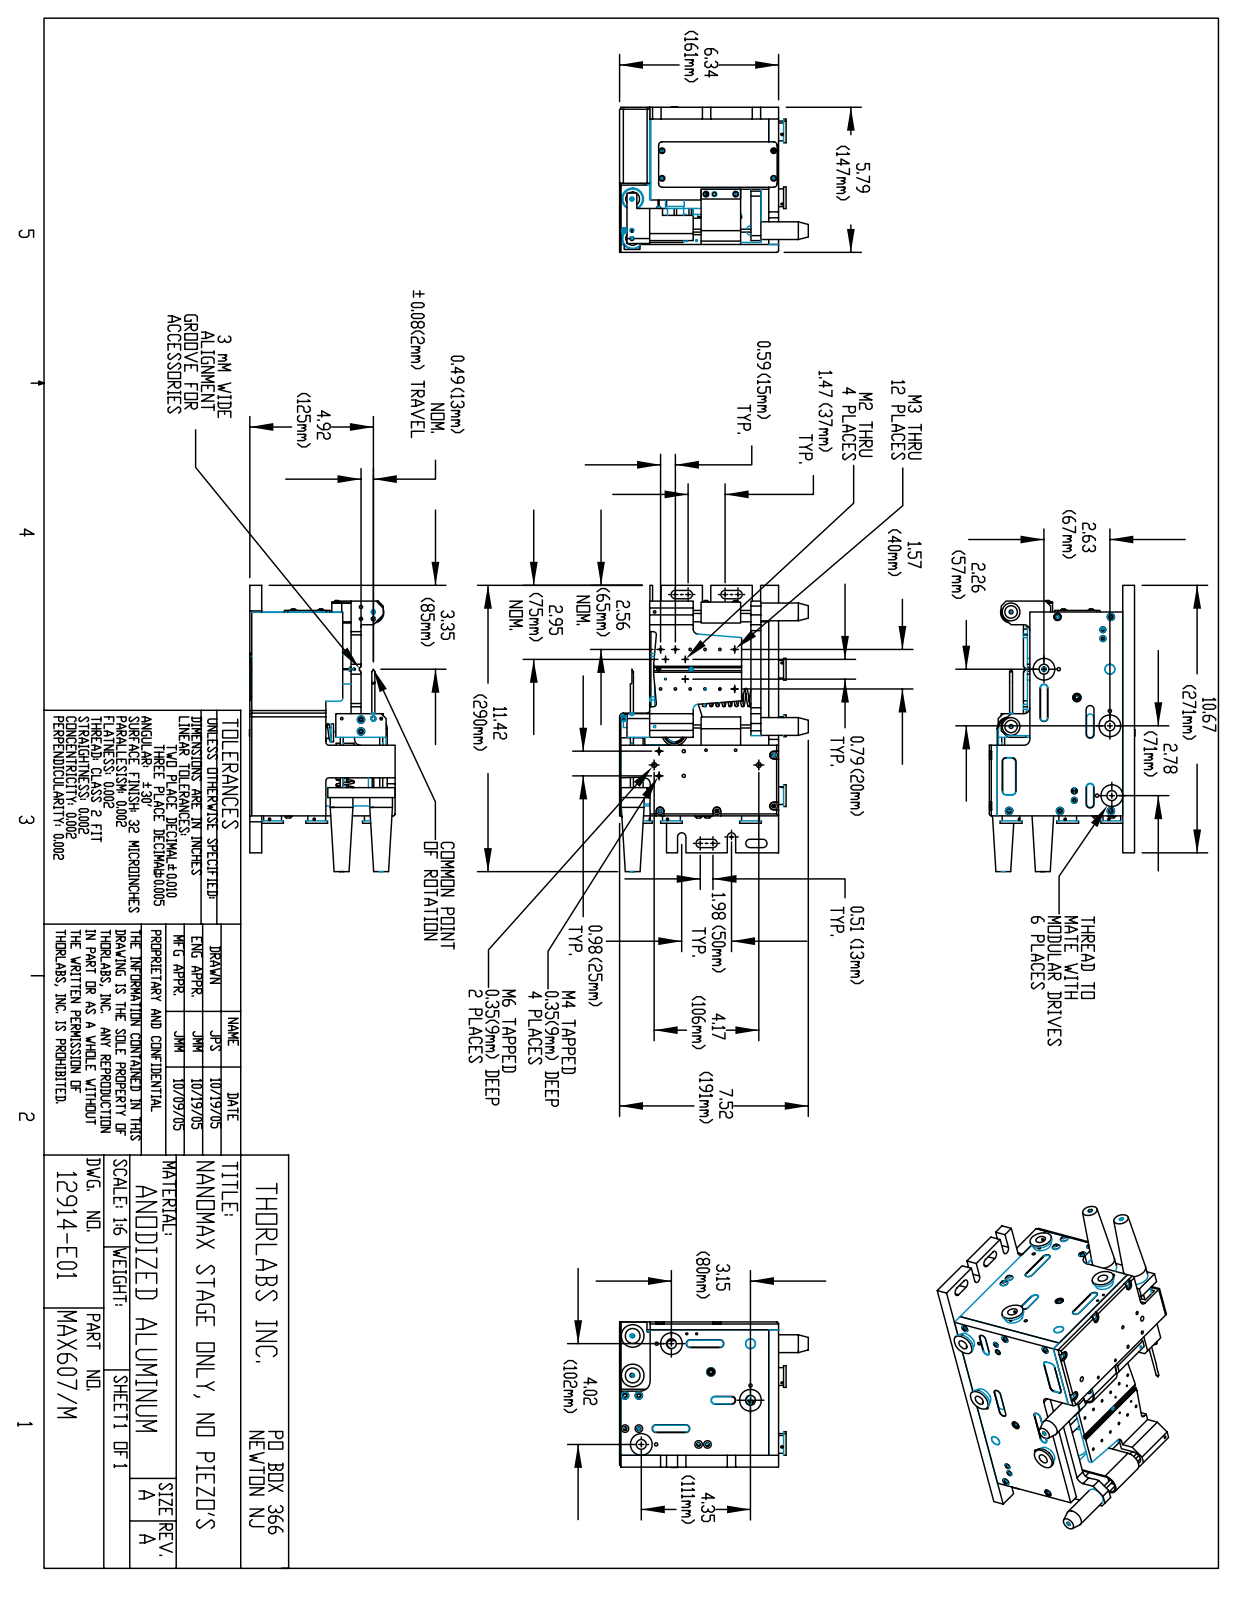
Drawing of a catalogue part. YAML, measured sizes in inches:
part_name: "12914-E0W"
step_written_by: "SolidWorks 2007 (AUTOMOTIVE_DESIGN)"
units: inches
bodies: {solids: 0, faces: 1185, planar: 615, cylindrical: 410, other: 160}
overall_size: [11.417, 7.52, 5.803]
round_holes:
  - {diameter: 0.098, count: 24}
  - {diameter: 0.295, count: 14}
  - {diameter: 0.13, count: 9}
  - {diameter: 0.394, count: 7}
  - {diameter: 0.236, count: 6}
  - {diameter: 0.291, count: 5}
  - {diameter: 0.063, count: 4}
  - {diameter: 0.126, count: 4}
  - {diameter: 0.157, count: 4}
  - {diameter: 0.551, count: 4}
  - {diameter: 0.081, count: 3}
  - {diameter: 0.335, count: 3}
round_bosses_or_shafts:
  - {diameter: 0.709, count: 11}
  - {diameter: 0.299, count: 8}
  - {diameter: 0.866, count: 6}
  - {diameter: 0.224, count: 6}
  - {diameter: 0.118, count: 6}
  - {diameter: 0.315, count: 5}
  - {diameter: 0.276, count: 4}
  - {diameter: 0.425, count: 3}
partial_cylinders:
  - {radius: 0.157, count: 15}
  - {radius: 0.167, count: 13}
  - {radius: 0.236, count: 8}
  - {radius: 0.118, count: 6}
  - {radius: 0.138, count: 6}
  - {radius: 0.079, count: 2}
  - {radius: 0.15, count: 2}
  - {radius: 0.197, count: 2}
face_to_face_distances: [0.394, 0.472, 0.047, 1.201, 0.315, 0.709, 4.429, 7.006, 8.13, 4.035]
hole_center_spacings: [0.591, 1.969, 1.682, 1.575, 1.181, 1.772, 2.37, 0.44]
